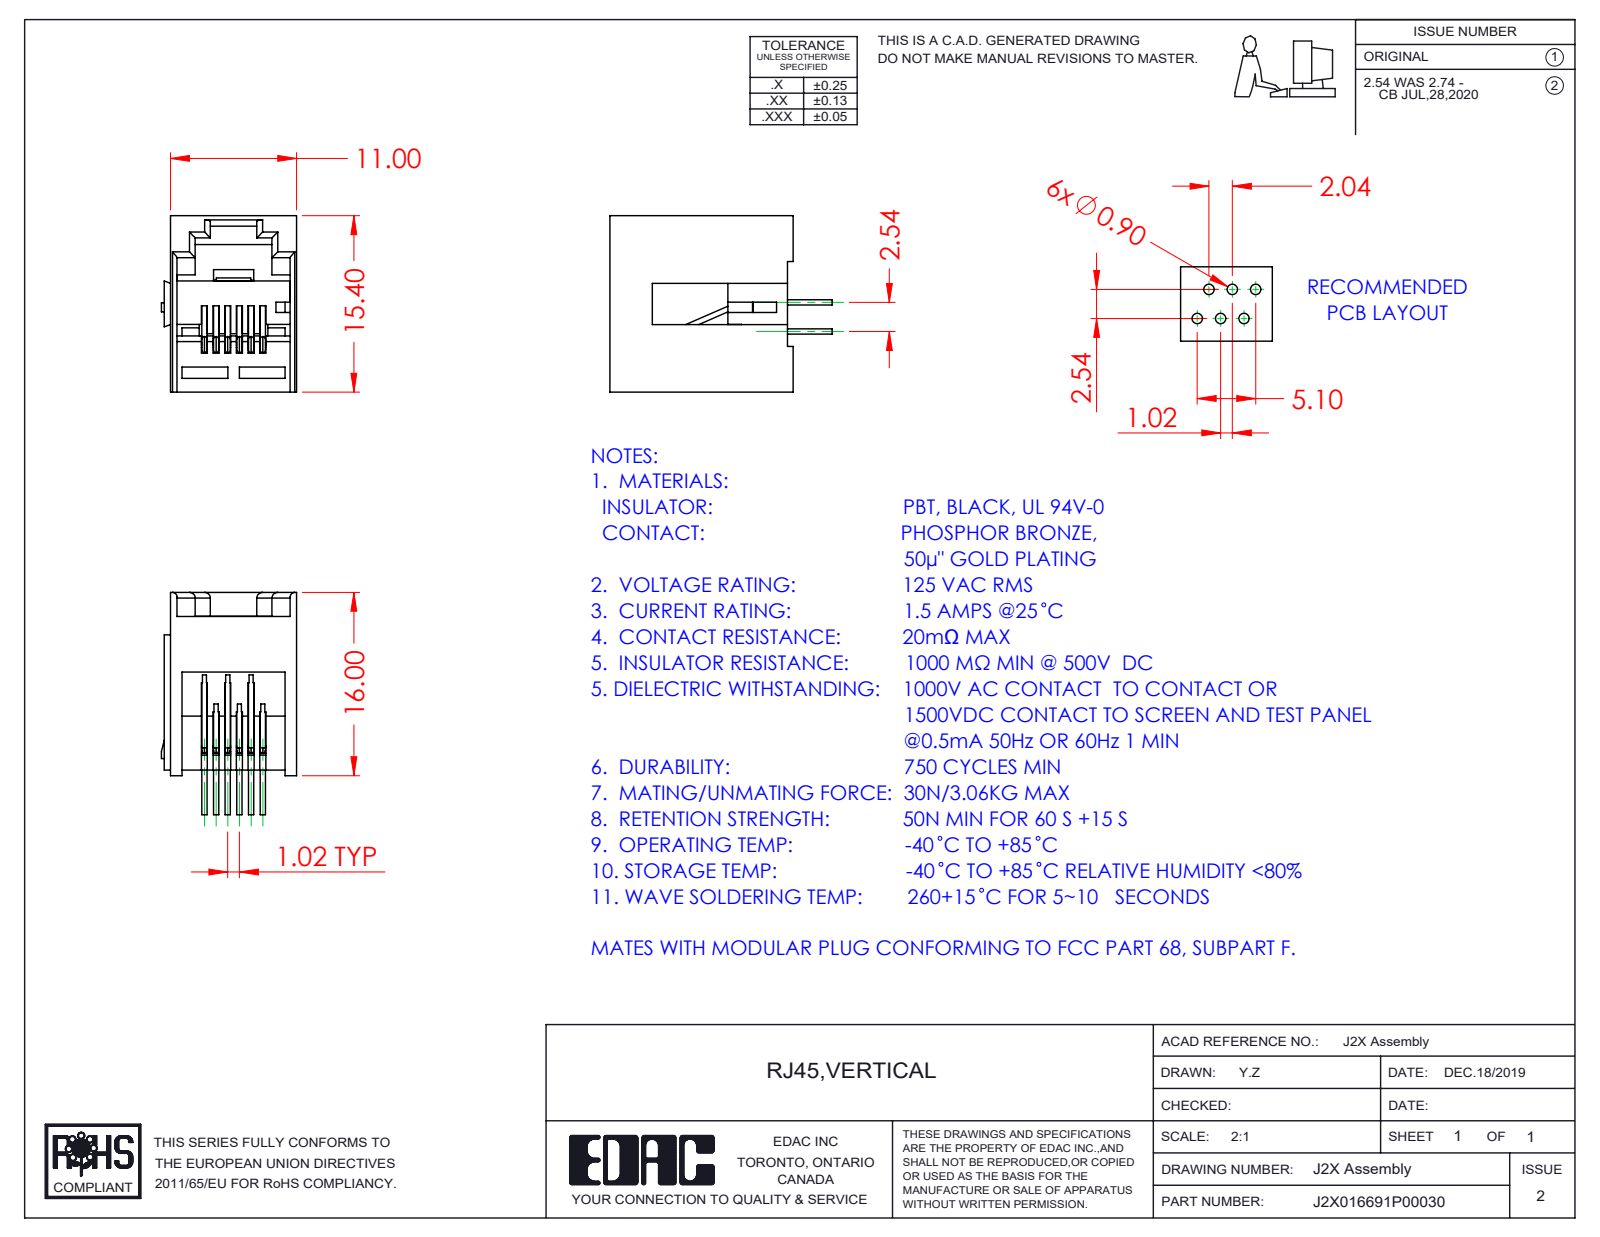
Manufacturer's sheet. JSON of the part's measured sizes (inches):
{"part_name": "J2X016691P00030; 2X Contacts_6P6C; 2X Contact Lock; 2X Insulator", "step_written_by": "SolidWorks 2020 (CONFIG_CONTROL_DESIGN)", "units": "inches", "bodies": {"solids": 8, "faces": 466, "planar": 333, "cylindrical": 97, "other": 36}, "overall_size": [0.764, 0.606, 0.465], "volume_in3": 0.074, "surface_area_in2": 4.408, "round_bosses_or_shafts": [[0.018, 24]], "partial_cylinders_radius": [[0.02, 7], [0.006, 2], [0.012, 2], [0.016, 2], [0.008, 1]], "face_to_face_distances": [0.039, 0.433, 0.08, 0.04, 0.02, 0.022, 0.02, 0.394, 0.472, 0.411]}
